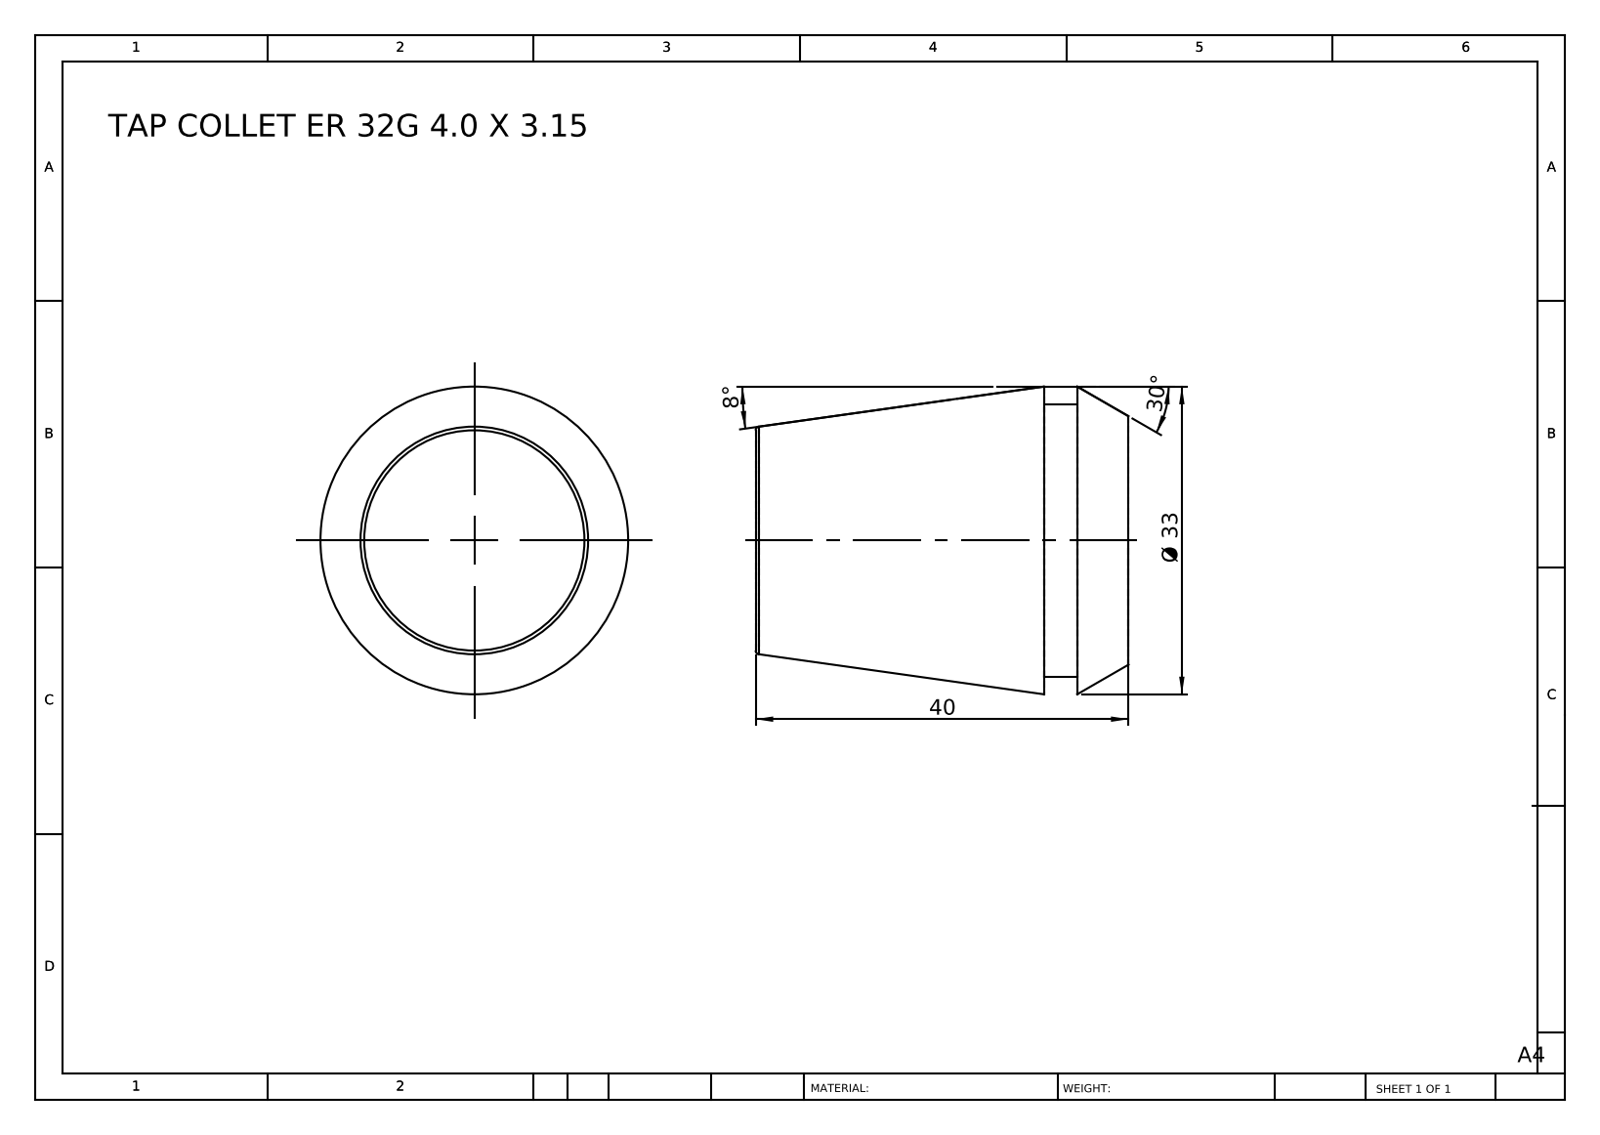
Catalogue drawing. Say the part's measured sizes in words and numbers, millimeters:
The part is named "TAP COLLET ER 32G 4.0 X 3.15". Its 3-D file was written by "SolidWorks 2014 (CONFIG_CONTROL_DESIGN)". It is 1 solid with 12 faces: 4 planar, 2 cylindrical and 6 other. Overall it measures 40 by 33 by 33 millimeters. Its volume is 26 350 cubic millimeters and its surface area 5 119 square millimeters. Round bosses or shafts: 1 of diameter 29.2. The main face-to-face distances are 40, 9.1, 30.9, 5.5, 3.6, 34.5.
